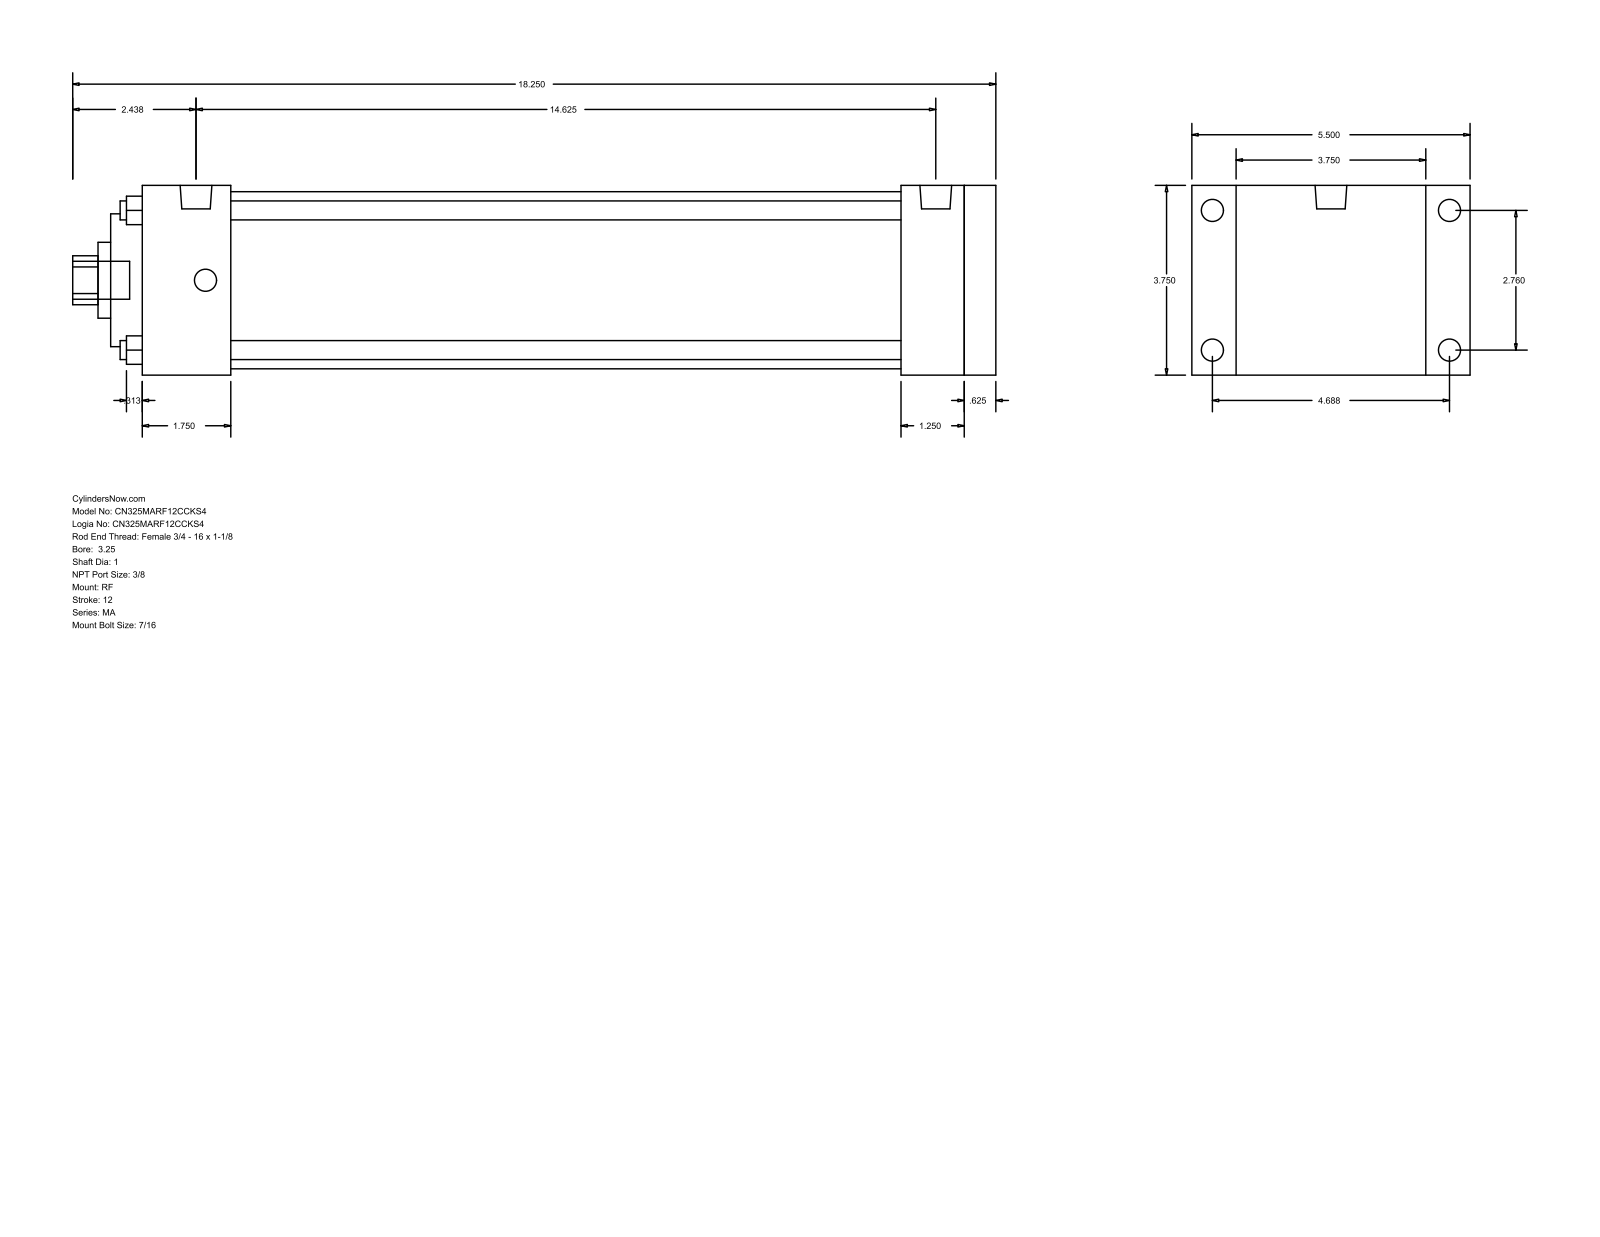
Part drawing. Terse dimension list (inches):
name: MA_RF__0325_1
written by: GSSL Pune (CONFIG_CONTROL_DESIGN)
unit: in
bodies: 0 solids, 94 faces (65 planar, 29 cylindrical, 0 other)
size: 18.25 × 5.5 × 3.75
holes: 4× ⌀0.375, 1× ⌀1, 1× ⌀1.5, 1× ⌀2.625, 1× ⌀3.5
bosses: 8× ⌀0.437, 2× ⌀0.627, 1× ⌀0.75
rounds: 1× R0.484
face distances: 3.75, 16.875, 0.625, 16.25, 0.875, 4.625, 15, 1.25, 1.875, 1.75
hole spacings: 1.952, 2.76, 3.903
